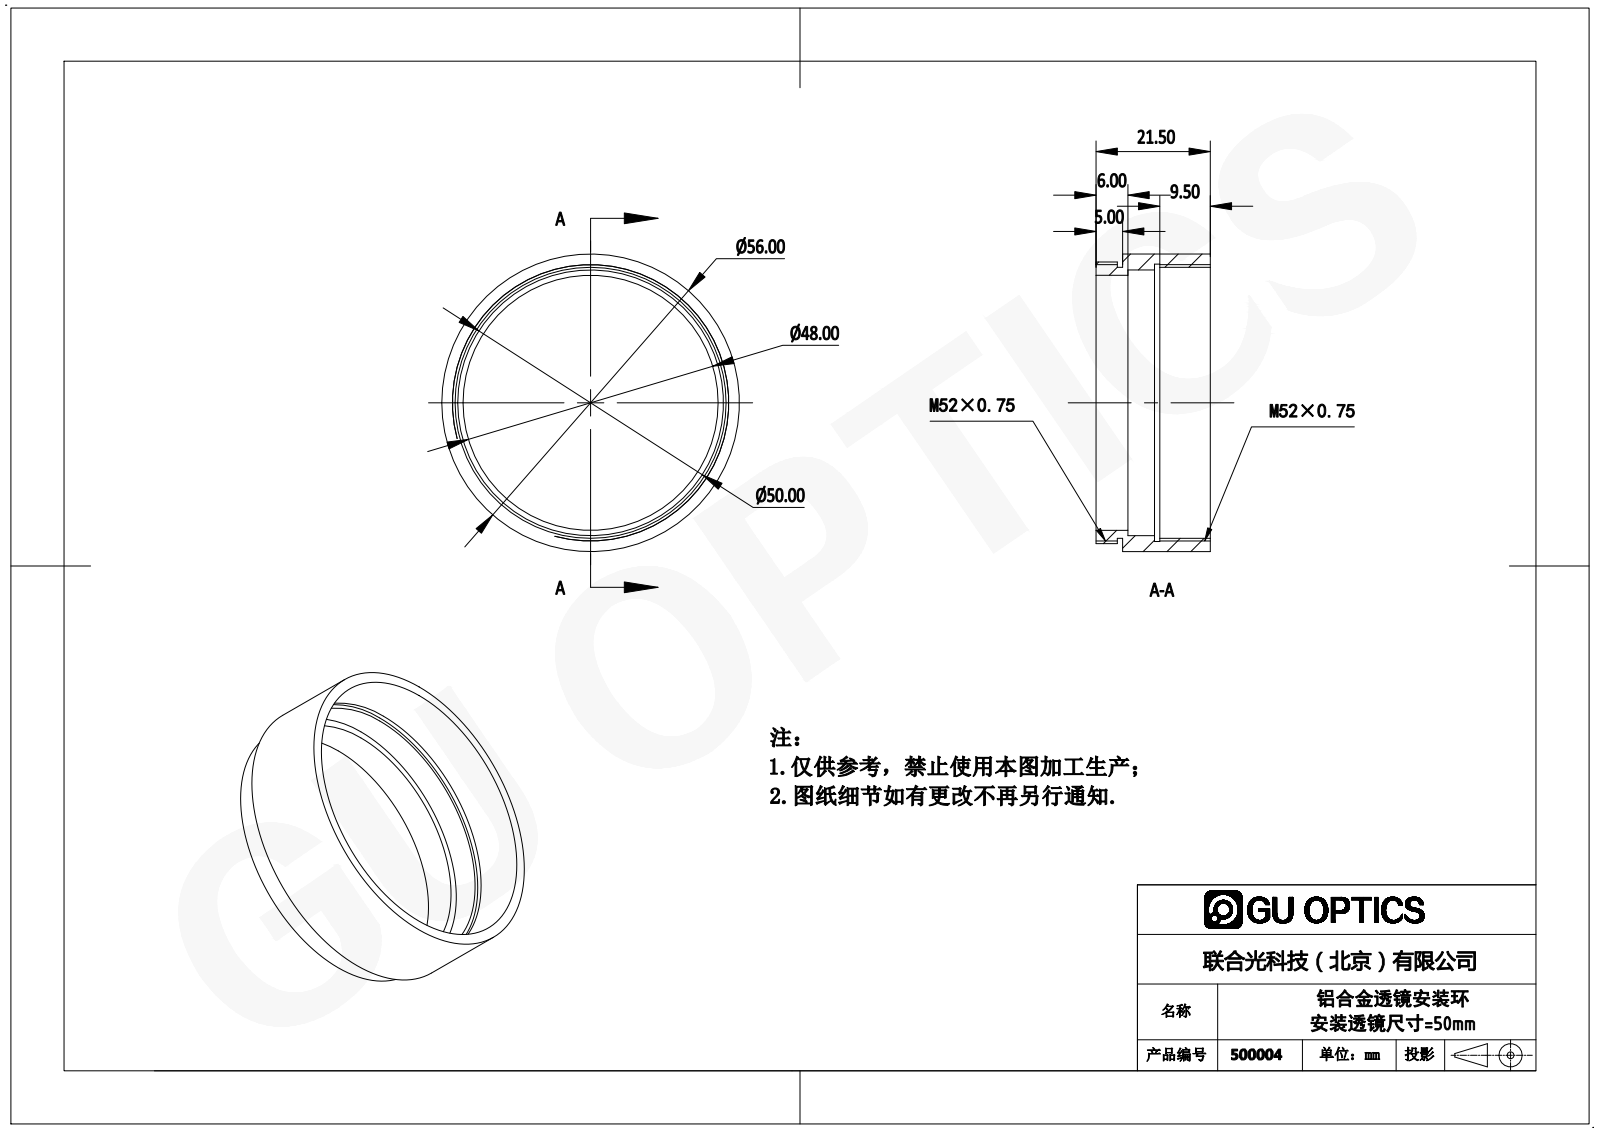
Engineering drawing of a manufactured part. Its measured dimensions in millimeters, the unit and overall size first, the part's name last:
Units: millimetres
Overall size (bounding box): 56 × 56 × 21.5
Round holes (diameter × count): ⌀48 ×1, ⌀50 ×1, ⌀51 ×1, ⌀52.2 ×1
Round bosses / shafts (diameter × count): ⌀56 ×1, ⌀53 ×1
Main face-to-face distances: 5, 6, 16.5, 1, 21.5, 7, 11, 10.5, 4, 17.5
Volume: 9 285 mm³ · Surface area: 8 934 mm²
Bodies: 1 solid, 21 faces (7 planar, 14 cylindrical, 0 other)
Part name (STEP PRODUCT): 500004
STEP written by: SolidWorks 2016 (AUTOMOTIVE_DESIGN)
